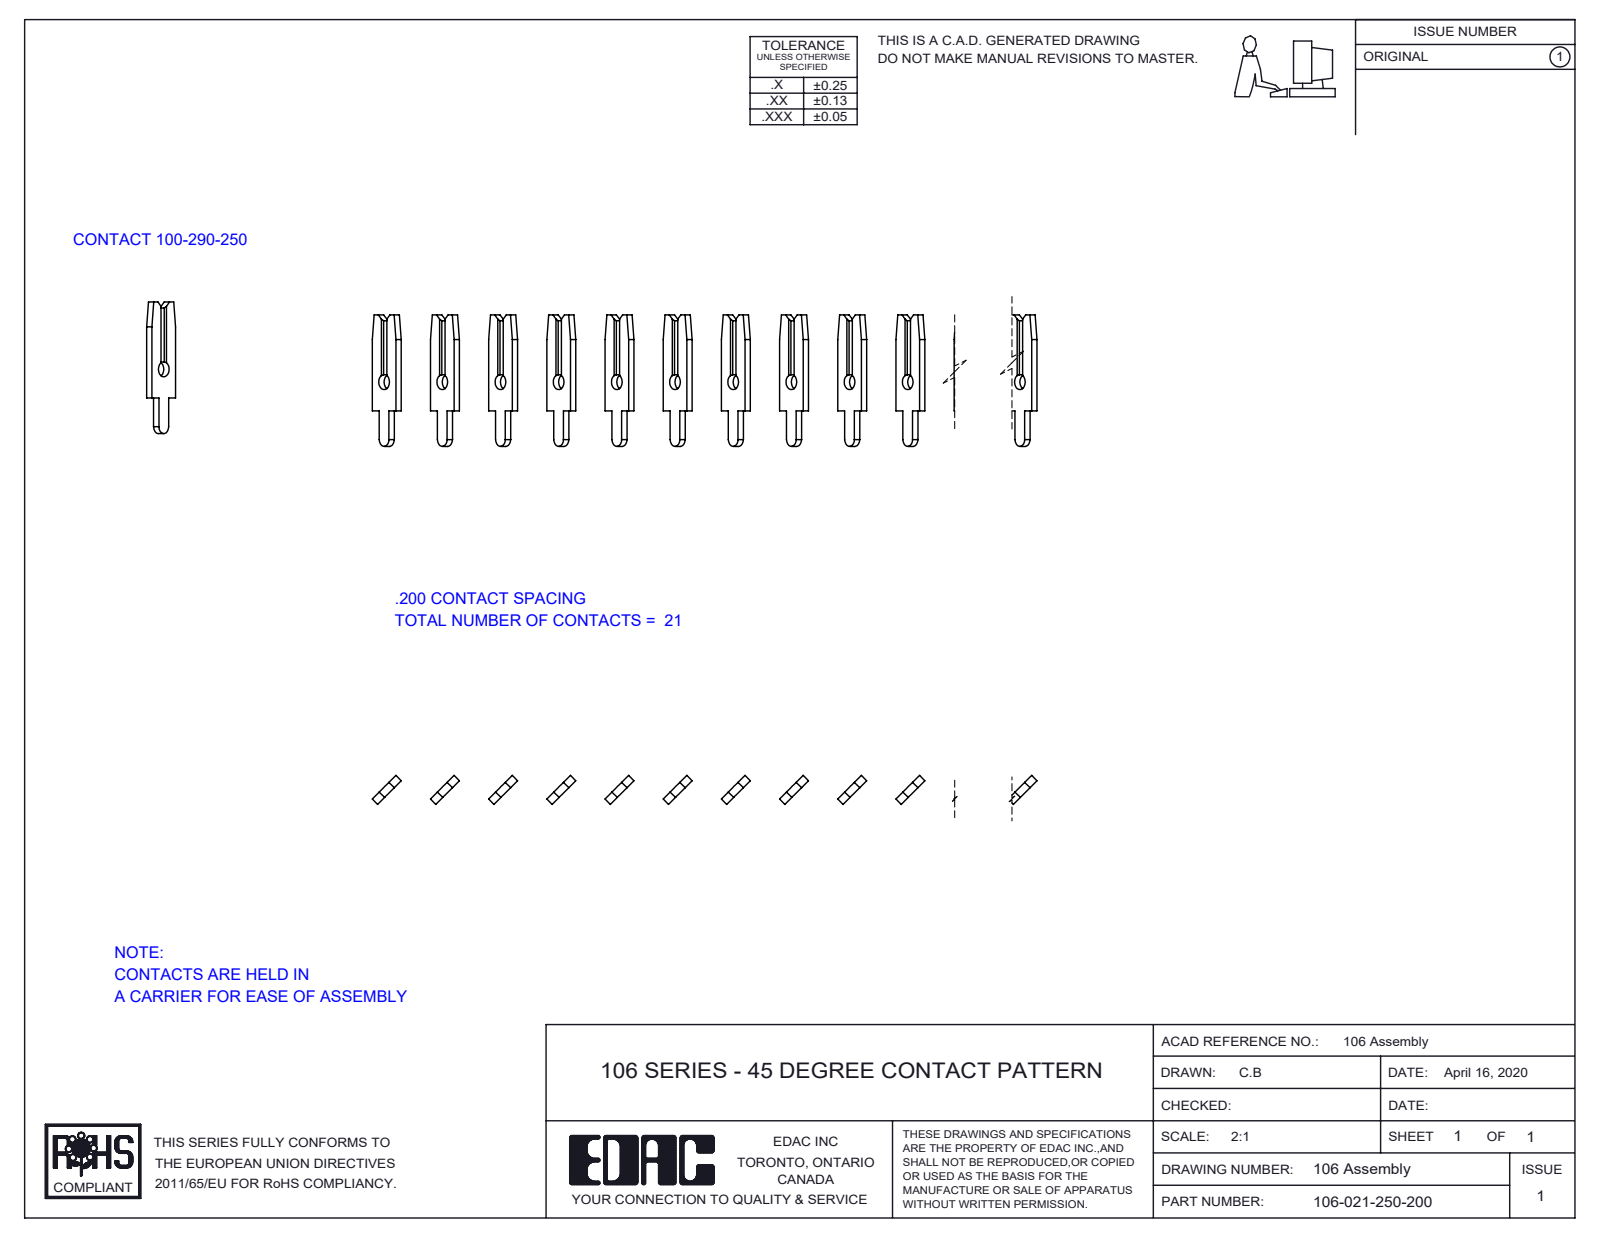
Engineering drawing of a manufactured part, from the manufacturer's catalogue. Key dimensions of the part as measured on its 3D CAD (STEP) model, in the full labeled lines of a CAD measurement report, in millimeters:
Part name (STEP PRODUCT): 106-021-250-200; 100-290-001_100-290-250
STEP written by: SolidWorks 2016 (CONFIG_CONTROL_DESIGN)
Units: millimetres
Bodies: 21 solids, 504 faces (420 planar, 84 cylindrical, 0 other)
Overall size (bounding box): 104.1 × 11.5 × 2.5
Volume: 330 mm³ · Surface area: 1 541 mm²
Round holes (diameter × count): ⌀1.3 ×21
Partial cylindrical surfaces — rounded edges, fillets, slot ends (radius × count): R0.6 ×21
Main face-to-face distances: 3.6, 21.5, 7.2, 18, 25.1, 14.4, 10.8, 28.7, 10.8, 39.5
Hole centre spacings: 3.6, 7.2, 10.8, 21.5, 25.1, 28.7, 39.5, 43.1
